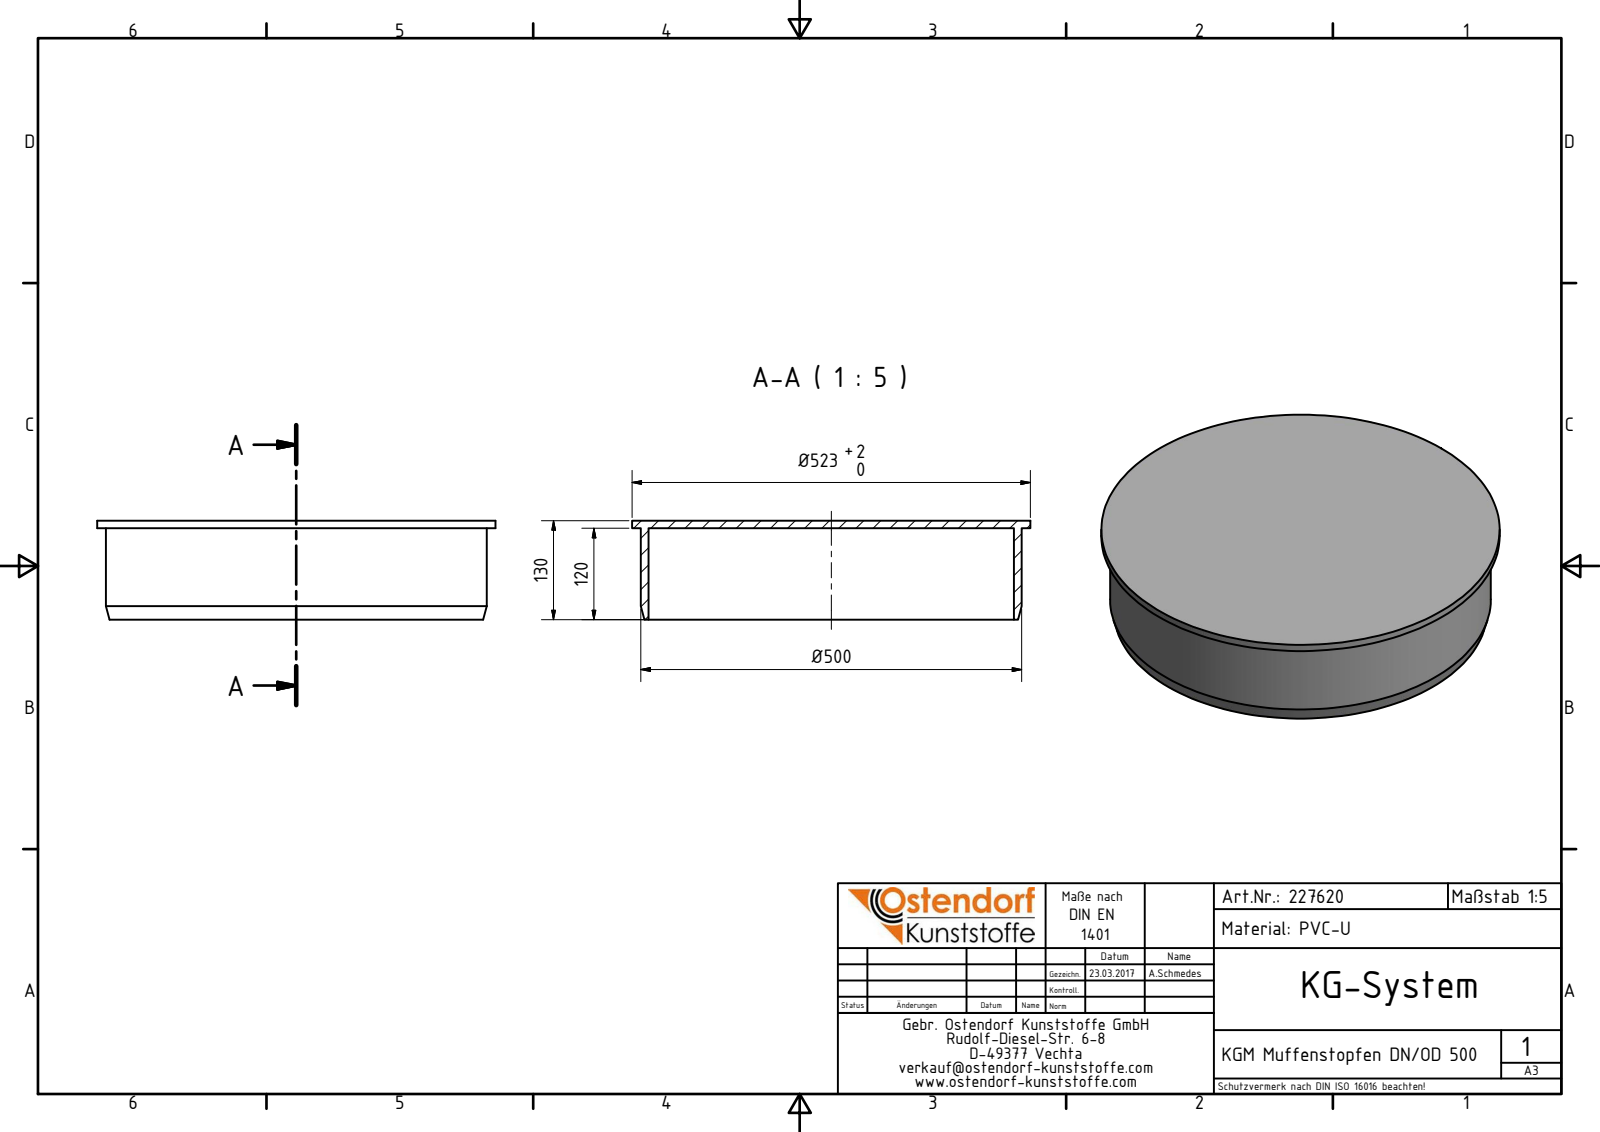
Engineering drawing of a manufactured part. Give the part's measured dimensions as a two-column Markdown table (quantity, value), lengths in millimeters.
| quantity | value |
| --- | --- |
| part name | 227620 KGM Muffenstopfen DN_OD 500 |
| STEP written by | Autodesk Inventor 2016 (AUTOMOTIVE_DESIGN) |
| units | millimeters |
| bodies | 1 solid, 8 faces (4 planar, 3 cylindrical, 1 other) |
| overall size | 523 × 523 × 130 |
| volume | 3 928 000 mm³ |
| surface area | 808 752 mm² |
| round holes (diameter × count) | 480 × 1 |
| round bosses / shafts (diameter × count) | 523 × 1, 500 × 1 |
| main face-to-face distances | 10, 120, 130 |
